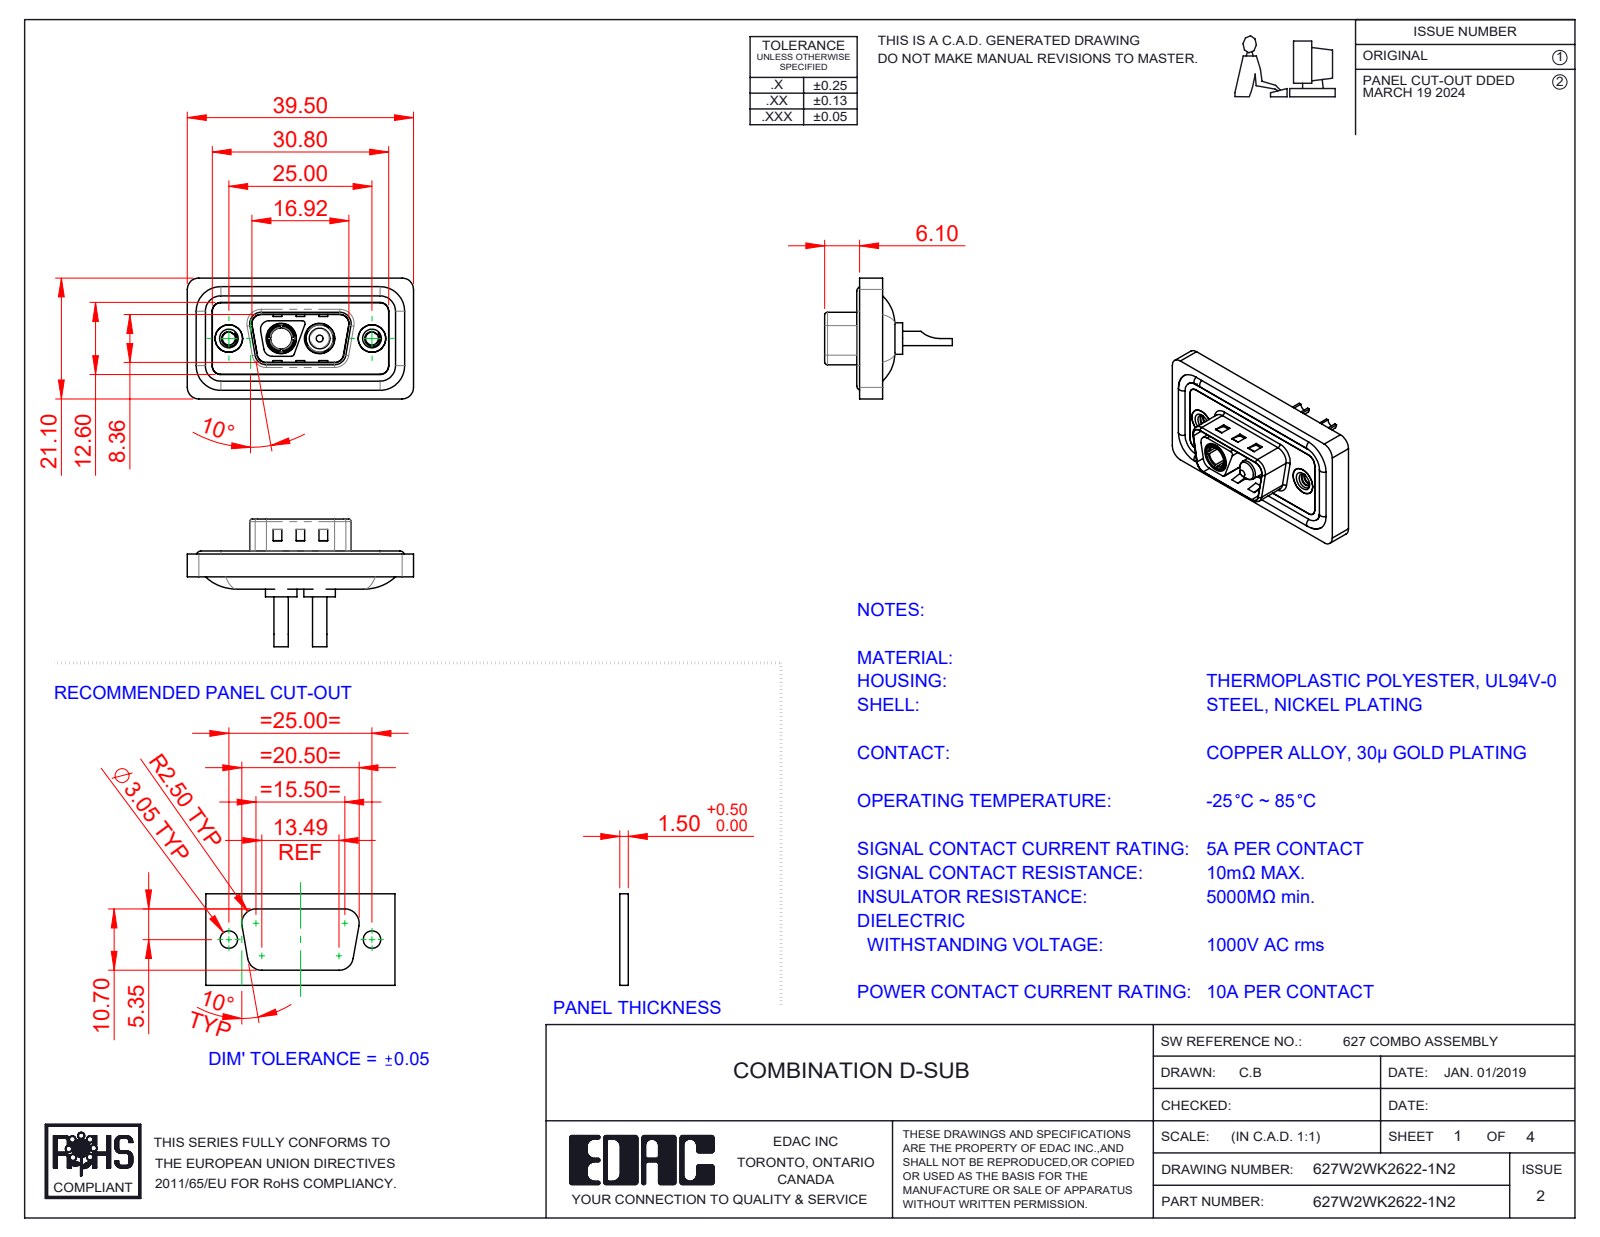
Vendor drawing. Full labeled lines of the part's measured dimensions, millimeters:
Part name (STEP PRODUCT): 627Combo Housing_2WK2; 627Combo Threaded Rivet_2; 627Combo Shell Rear_09 Contacts; 627Combo Waterproof Housing_09 Contacts (+4 more)
STEP written by: SolidWorks 2023 (CONFIG_CONTROL_DESIGN)
Units: millimetres
Bodies: 11 solids, 546 faces (193 planar, 233 cylindrical, 120 other)
Overall size (bounding box): 39.5 × 22.3 × 21.1
Volume: 4 549 mm³ · Surface area: 7 438 mm²
Round holes (diameter × count): ⌀1.7 ×2, ⌀2.26 ×2, ⌀4 ×2, ⌀4.8 ×2, ⌀4.85 ×2, ⌀5 ×2, ⌀5.3 ×2, ⌀3.7 ×1
Round bosses / shafts (diameter × count): ⌀1.6 ×4, ⌀5.5 ×2, ⌀5.2 ×2, ⌀4.9 ×2, ⌀4.75 ×2, ⌀3.75 ×2, ⌀2.5 ×2, ⌀4.96 ×1
Partial cylindrical surfaces — rounded edges, fillets, slot ends (radius × count): R1.5 ×24, R2 ×18, R0.5 ×10, R1.6 ×8, R0.25 ×4, R0.6 ×4, R0.65 ×4, R0.9 ×4
Main face-to-face distances: 0.4, 1.1, 2.9, 0.5, 3.1, 1.6, 1.5, 4, 2.5, 1.8
Hole centre spacings: 9.14, 15.86, 6.72, 25
